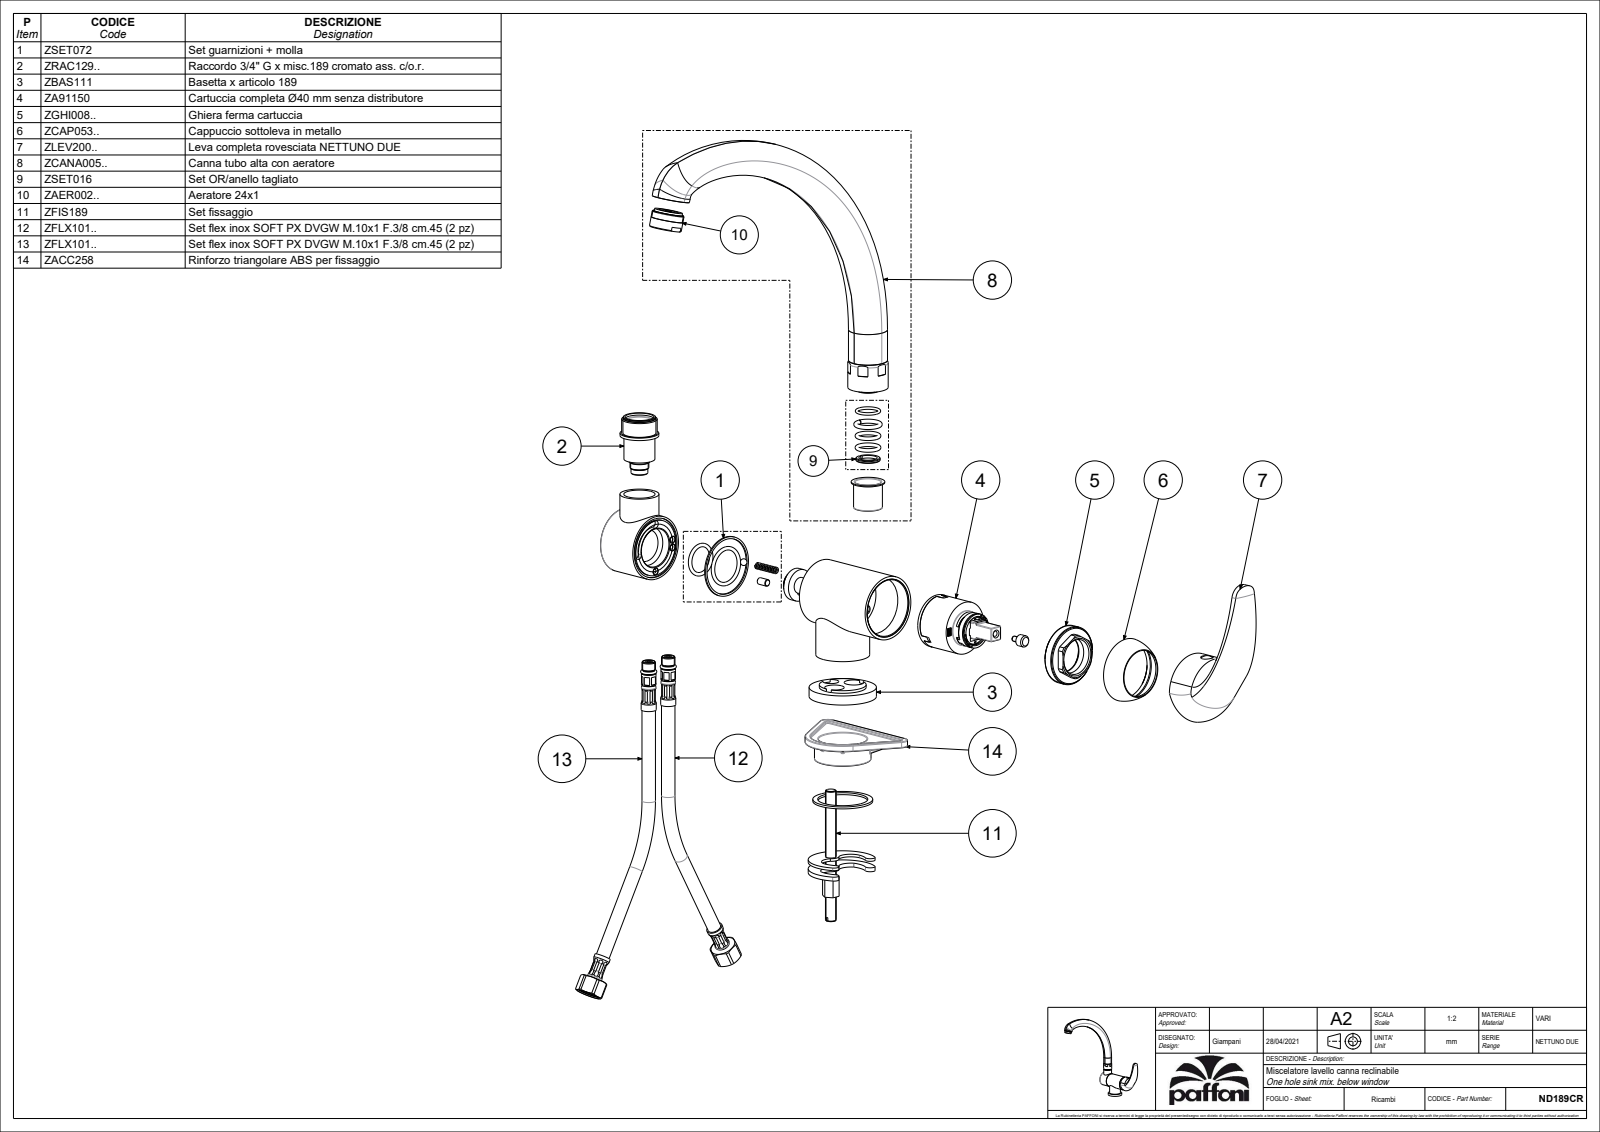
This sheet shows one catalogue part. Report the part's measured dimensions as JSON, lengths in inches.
{"part_name": "ND189CR", "step_written_by": "CREO PARAMETRIC BY PTC INC, 2020044 (CONFIG_CONTROL_DESIGN)", "units": "inches", "bodies": {"solids": 2, "faces": 156, "planar": 57, "cylindrical": 38, "other": 61}, "overall_size": [12.137, 9.686, 6.535], "volume_in3": 31.94, "surface_area_in2": 121.4, "round_holes": [[0.236, 1], [0.717, 1], [0.728, 1], [0.835, 1], [1.063, 1]], "round_bosses_or_shafts": [[0.945, 2], [1.969, 1], [1.89, 1], [1.575, 1], [1.181, 1], [1.142, 1], [1.134, 1], [1.039, 1]], "partial_cylinders_radius": [[0.154, 1], [0.157, 1]], "face_to_face_distances": [0.276, 4.46, 4.185, 0.02, 4.441, 4.165, 0.602, 3.643, 3.367, 0.798], "hole_center_spacings": [4.173]}
